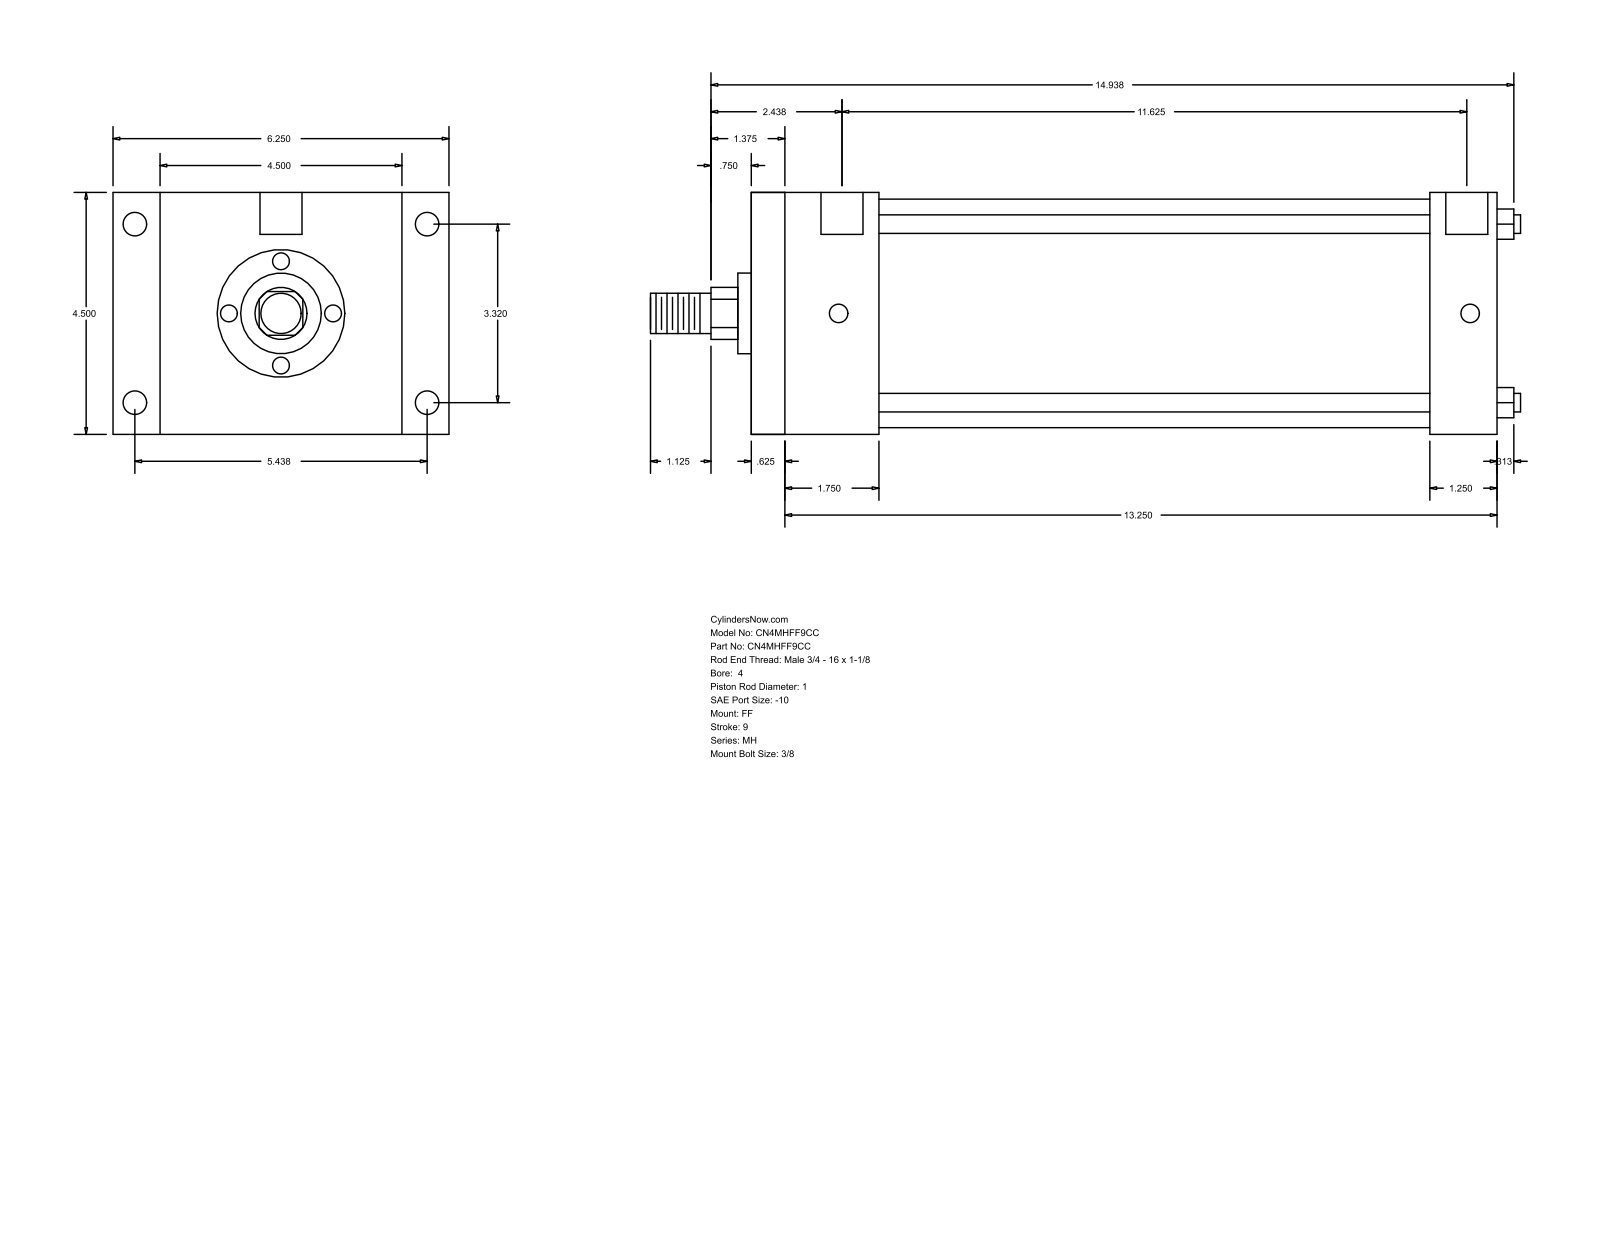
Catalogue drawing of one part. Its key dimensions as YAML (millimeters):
part_name: "MH_FF__0400_1"
step_written_by: "GSSL Pune (CONFIG_CONTROL_DESIGN)"
units: millimeters
bodies: {solids: 0, faces: 92, planar: 64, cylindrical: 28, other: 0}
overall_size: [411.16, 158.75, 114.3]
round_holes:
  - {diameter: 8.73, count: 4}
  - {diameter: 11.13, count: 4}
  - {diameter: 19.84, count: 2}
round_bosses_or_shafts:
  - {diameter: 8.76, count: 4}
  - {diameter: 107.95, count: 1}
  - {diameter: 38.1, count: 1}
  - {diameter: 25.4, count: 1}
  - {diameter: 19.05, count: 1}
partial_cylinders:
  - {radius: 12.29, count: 1}
face_to_face_distances: [114.3, 352.43, 15.87, 336.56, 60.33, 44.46, 292.1, 320.68, 304.81, 260.35]
hole_center_spacings: [1.58, 84.32, 138.12, 161.82, 296.86, 298.44, 295.28]
